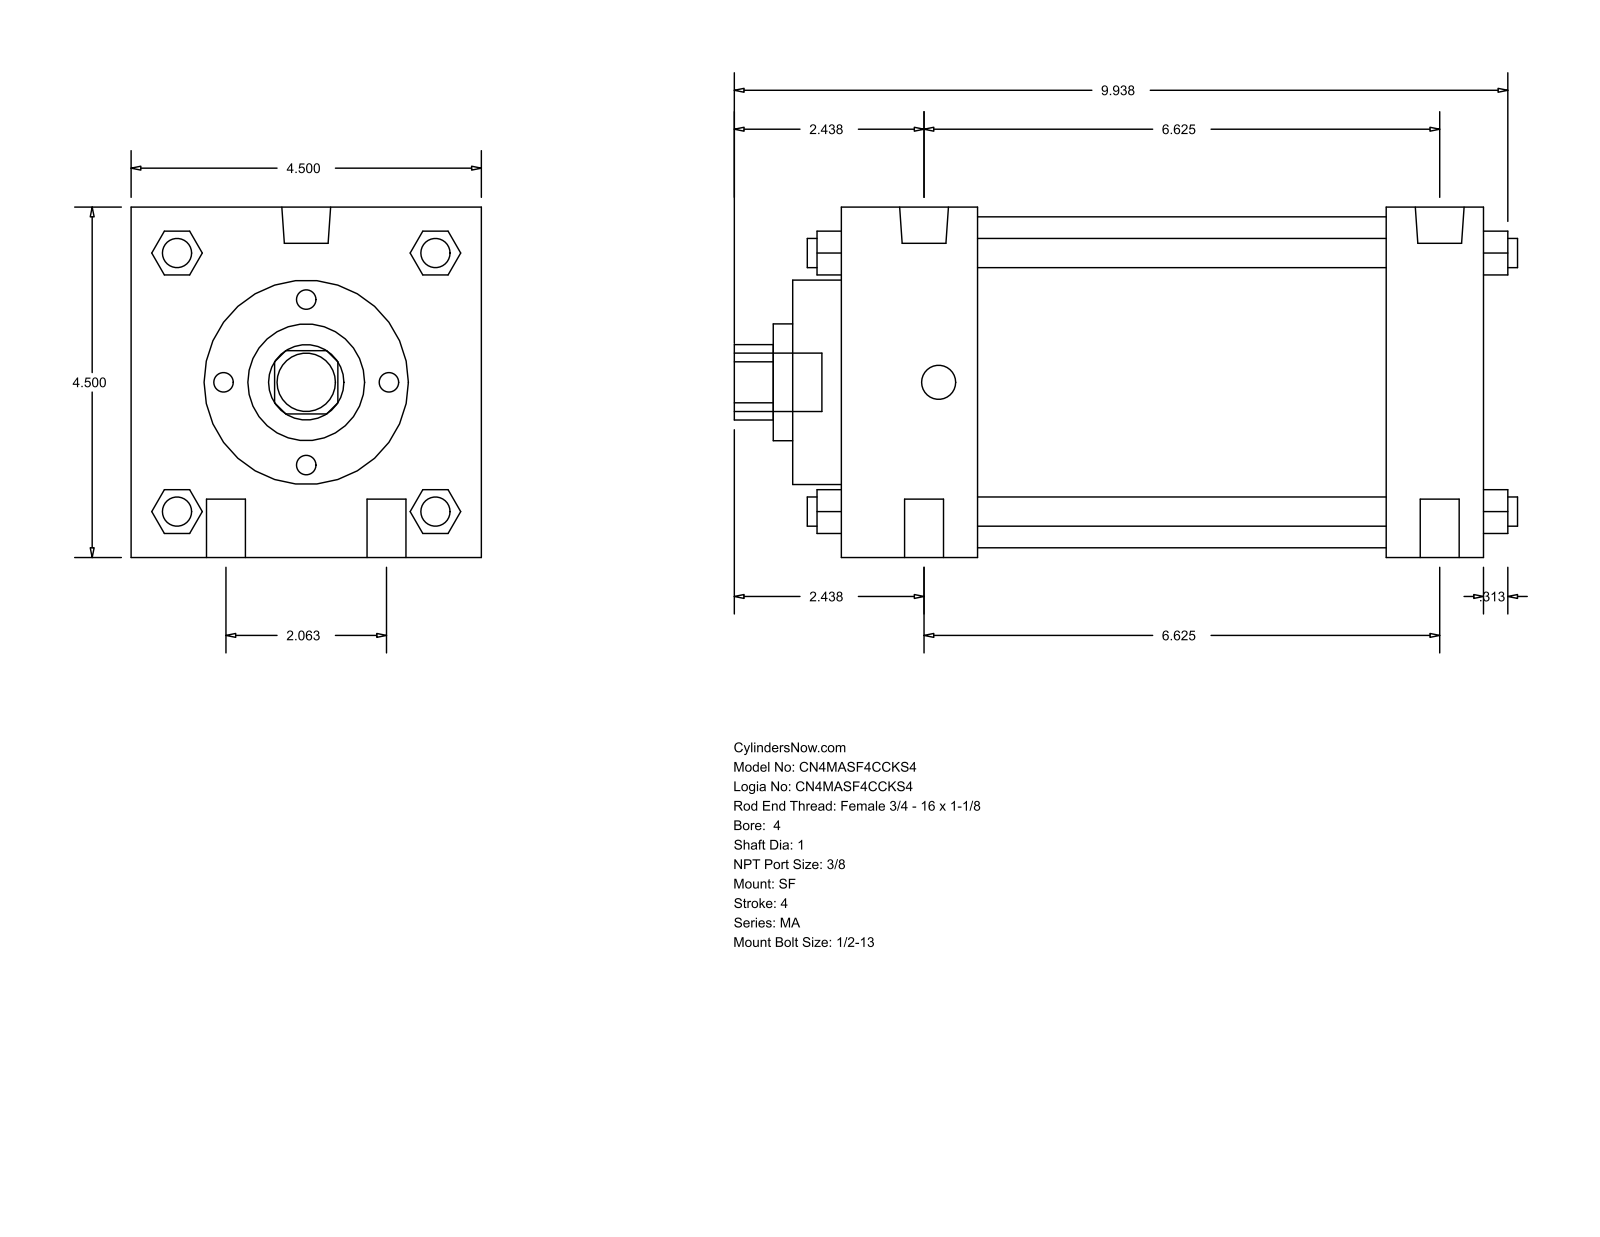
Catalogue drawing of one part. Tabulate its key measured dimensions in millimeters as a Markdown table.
| quantity | value |
| --- | --- |
| part name | MA_SF__0400_1 |
| STEP written by | GSSL Pune (CONFIG_CONTROL_DESIGN) |
| units | millimeters |
| bodies | 0 solids, 126 faces (95 planar, 31 cylindrical, 0 other) |
| overall size | 255.59 × 114.3 × 114.3 |
| round holes (diameter × count) | 25.4 × 1, 38.1 × 1, 66.67 × 1, 107.95 × 1 |
| round bosses / shafts (diameter × count) | 12.7 × 4, 9.53 × 4, 15.93 × 2, 11.11 × 2, 19.05 × 1 |
| partial cylindrical surfaces (radius × count) | 12.29 × 1 |
| main face-to-face distances | 114.3, 209.55, 177.8, 31.75, 44.46, 133.34, 165.09, 225.42, 15.87, 60.33 |
